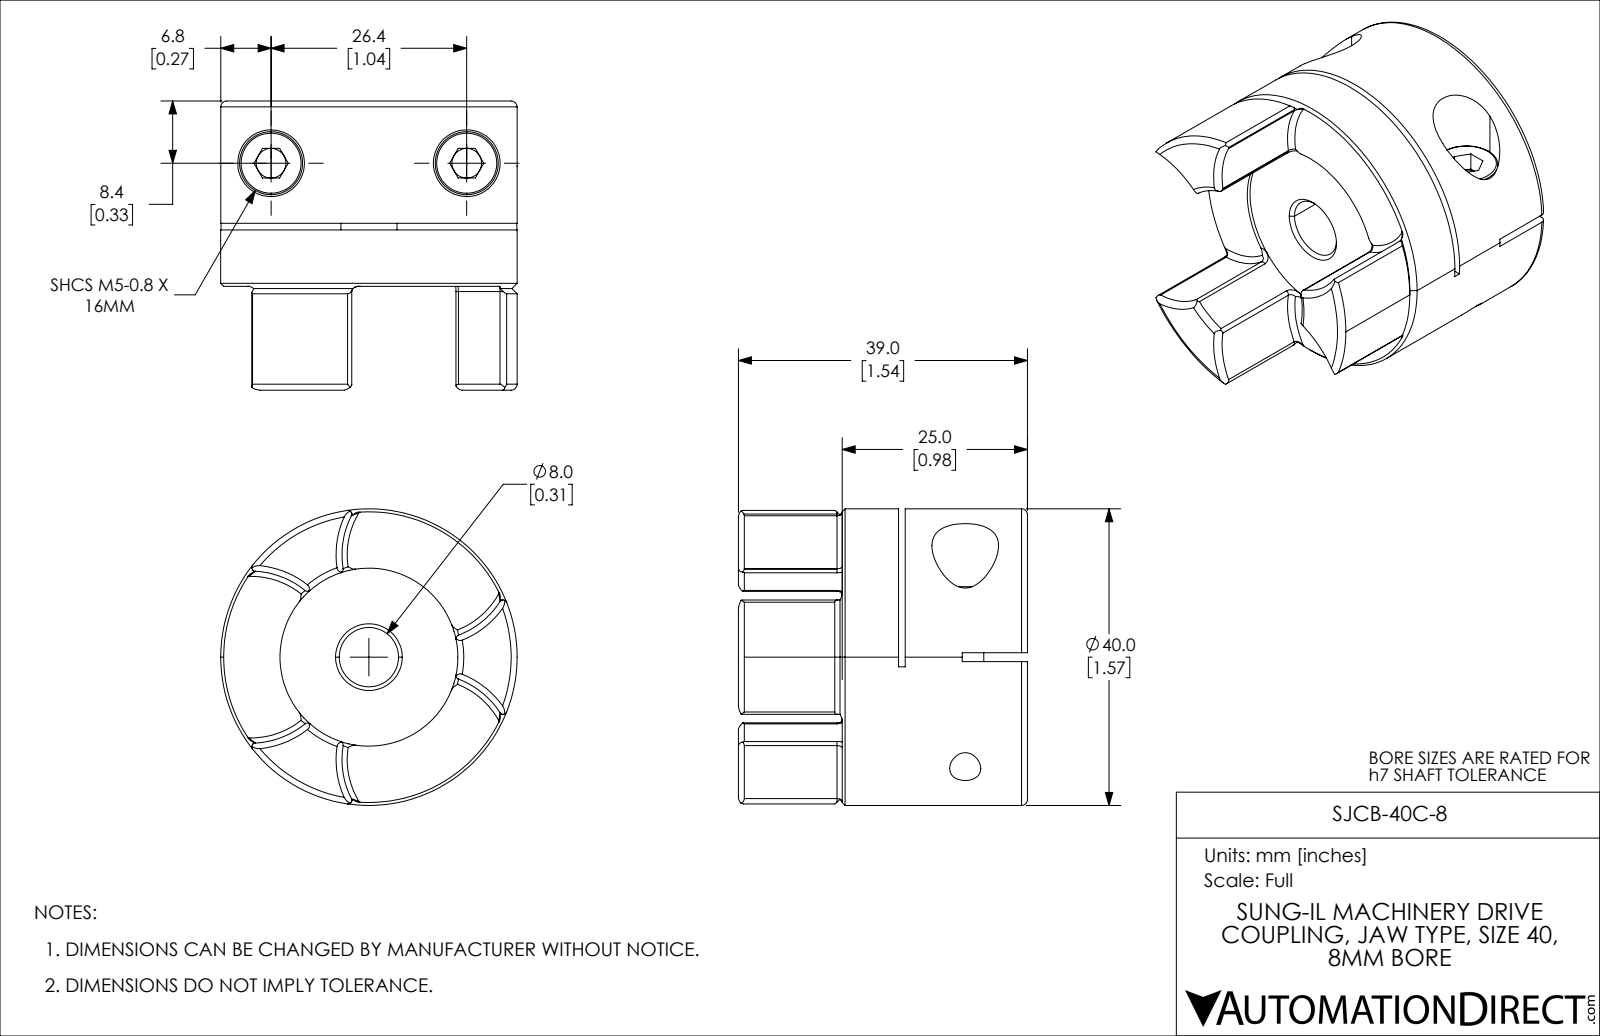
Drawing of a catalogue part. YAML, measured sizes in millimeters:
part_name: "SJCB-40C-8"
step_written_by: "SolidWorks 2021 (CONFIG_CONTROL_DESIGN)"
units: millimeters
bodies: {solids: 3, faces: 184, planar: 50, cylindrical: 68, other: 66}
overall_size: [40, 40, 39]
volume: 31380
surface_area: 11719
round_holes:
  - {diameter: 4, count: 2}
  - {diameter: 4.2, count: 2}
  - {diameter: 5.4, count: 2}
  - {diameter: 9, count: 2}
  - {diameter: 8, count: 1}
  - {diameter: 24, count: 1}
round_bosses_or_shafts:
  - {diameter: 8.5, count: 2}
  - {diameter: 5, count: 2}
  - {diameter: 40, count: 1}
partial_cylinders:
  - {radius: 0.5, count: 12}
  - {radius: 11.6, count: 3}
  - {radius: 40, count: 1}
face_to_face_distances: [17.4, 0.9, 16.5, 7.6, 8.5, 25, 1.2, 0.5, 7.1, 8]
hole_center_spacings: [26.4]
